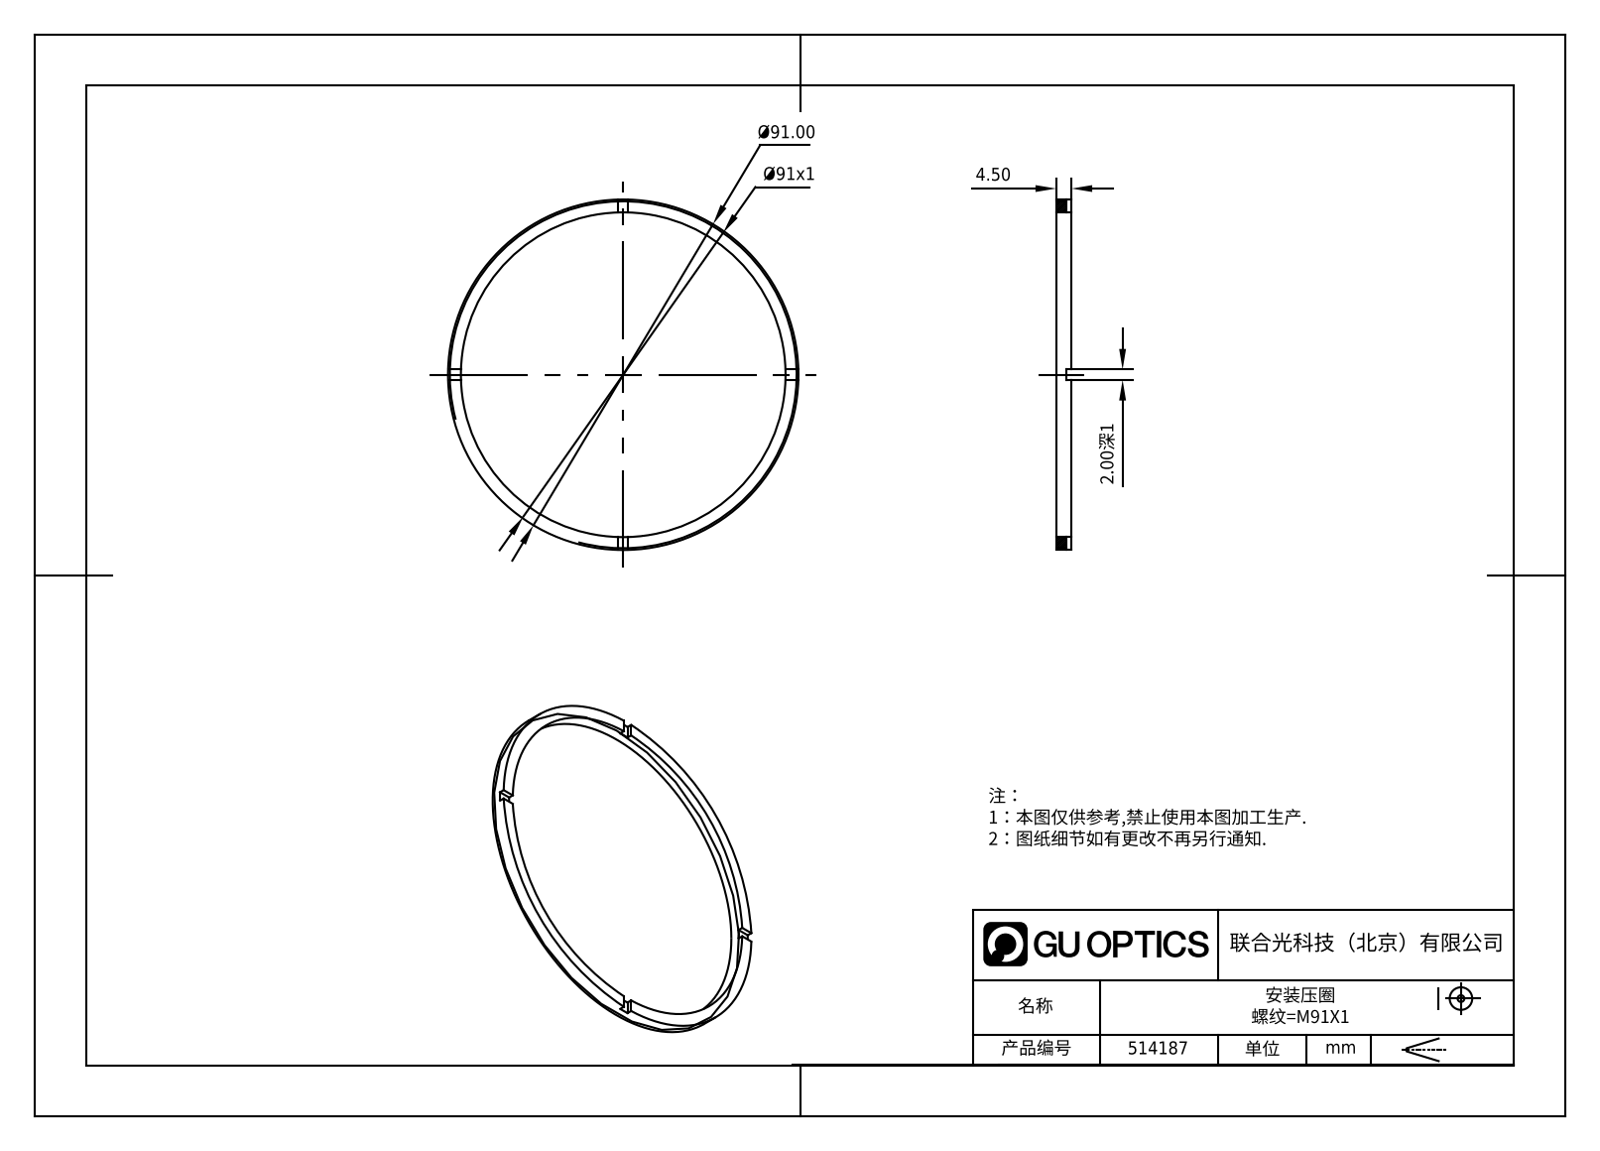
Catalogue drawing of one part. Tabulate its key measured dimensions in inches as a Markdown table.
| quantity | value |
| --- | --- |
| part name | 514187 |
| STEP written by | SolidWorks 2020 (CONFIG_CONTROL_DESIGN) |
| units | inches |
| bodies | 1 solid, 21 faces (17 planar, 4 cylindrical, 0 other) |
| overall size | 3.583 × 3.583 × 0.177 |
| volume | 0.263 in³ |
| surface area | 6.836 in² |
| round holes (diameter × count) | 3.307 × 1 |
| round bosses / shafts (diameter × count) | 3.583 × 1 |
| main face-to-face distances | 0.177, 0.138, 0.039, 0.079 |
